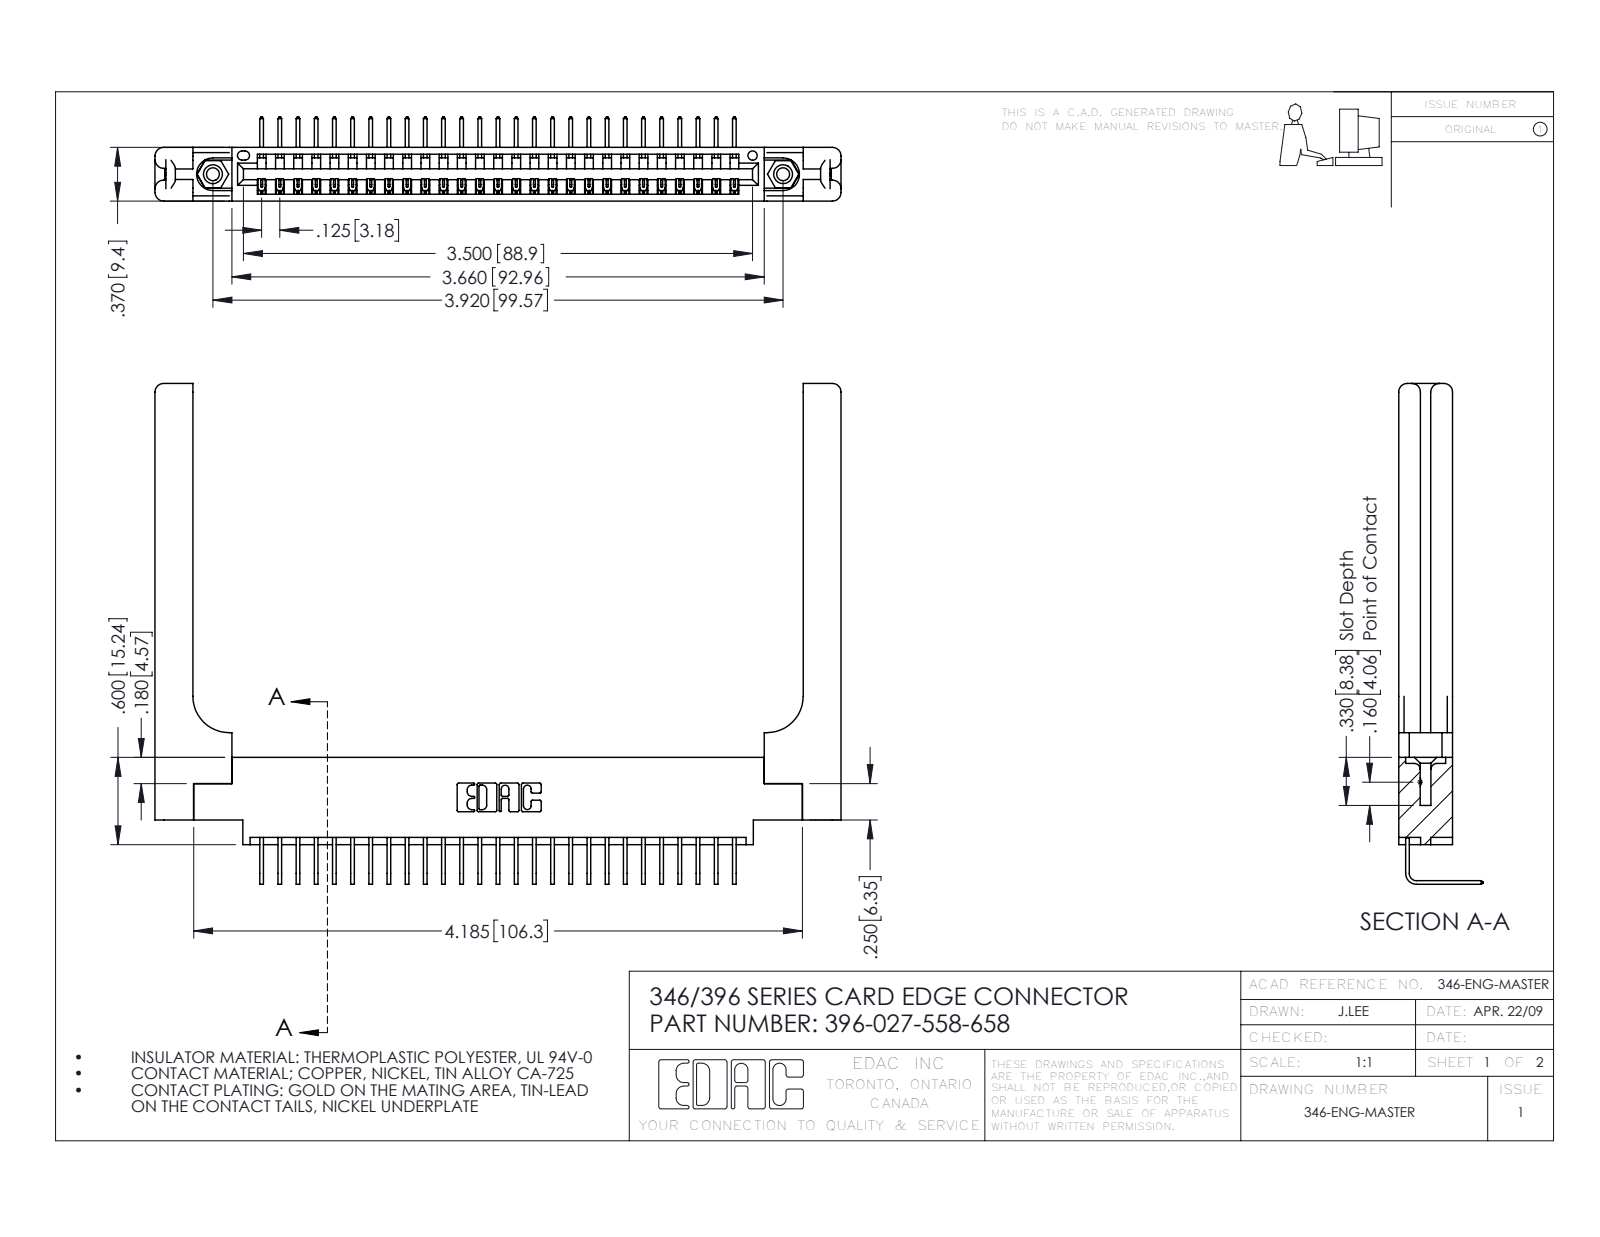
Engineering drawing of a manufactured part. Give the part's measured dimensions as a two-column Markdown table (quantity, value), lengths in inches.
| quantity | value |
| --- | --- |
| part name | 346-220-058_345-220-058; 346 Part_0.170 Offset - 0.156 Dia-TH; 396-027-558-658; 345-250-001_345-250-001-102 (+1 more) |
| STEP written by | SolidWorks 2016 (CONFIG_CONTROL_DESIGN) |
| units | inches |
| bodies | 32 solids, 2002 faces (1362 planar, 580 cylindrical, 60 other) |
| overall size | 4.716 × 3.443 × 0.58 |
| volume | 1.148 in³ |
| surface area | 30.73 in² |
| round holes (diameter × count) | 0.089 × 2, 0.125 × 2, 0.156 × 2, 0.064 × 1 |
| round bosses / shafts (diameter × count) | 0.155 × 2 |
| partial cylindrical surfaces (radius × count) | 0.006 × 54, 0.01 × 22, 0.06 × 16, 0.007 × 6, 0.031 × 6, 0.026 × 3, 0.03 × 2, 0.031 × 2 |
| main face-to-face distances | 0.37, 0.322, 0.072, 0.048, 0.148, 0.15, 0.025, 0.25, 0.298, 0.076 |
| hole center spacings | 0.246, 3.712, 3.92 |
